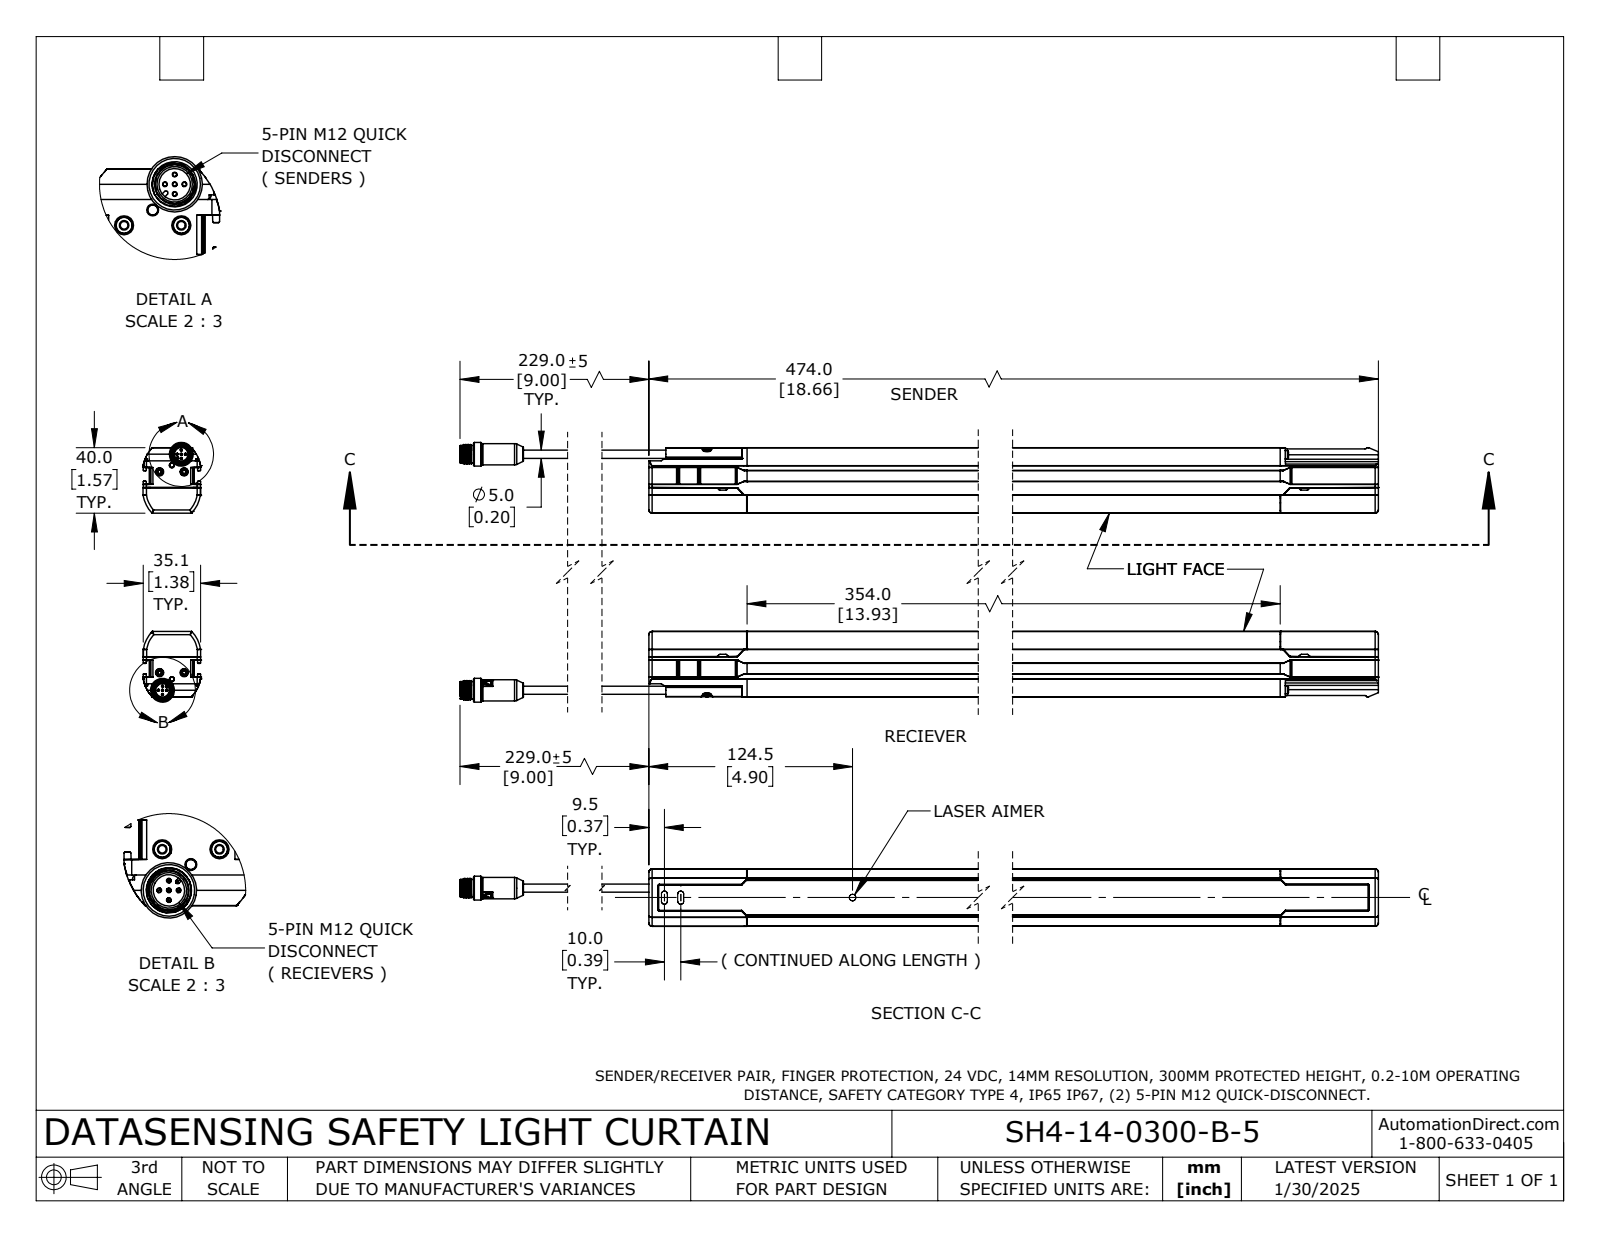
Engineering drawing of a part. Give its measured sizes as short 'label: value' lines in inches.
name: 957920001
written by: SolidWorks 2024 (AUTOMOTIVE_DESIGN)
unit: in
bodies: 4 solids, 2582 faces (1178 planar, 778 cylindrical, 626 other)
size: 21.154 × 6.248 × 1.384
volume: 42.72 in³; area: 266.2 in²
holes: 6× ⌀0.079, 6× ⌀0.118, 6× ⌀0.197, 2× ⌀0.101, 2× ⌀0.102, 2× ⌀0.102, 2× ⌀0.103, 2× ⌀0.11, 2× ⌀0.325, 2× ⌀0.382, 2× ⌀0.407, 2× ⌀0.425
bosses: 10× ⌀0.197, 10× ⌀0.039, 8× ⌀0.087, 6× ⌀0.172, 4× ⌀0.217, 2× ⌀0.571, 2× ⌀0.512, 2× ⌀0.417
rounds: 174× R0.01, 74× R0.016, 50× R0.02, 36× R0.008, 26× R0.031, 16× R0.047, 14× R0.079, 12× R0.031
face distances: 1.496, 4.496, 3, 0.079, 1.033, 0.083, 1.417, 4.575, 3.079, 1.413
hole spacings: 0.591, 0.866, 0.43, 0.434, 0.017, 0.429, 0.43, 0.431
